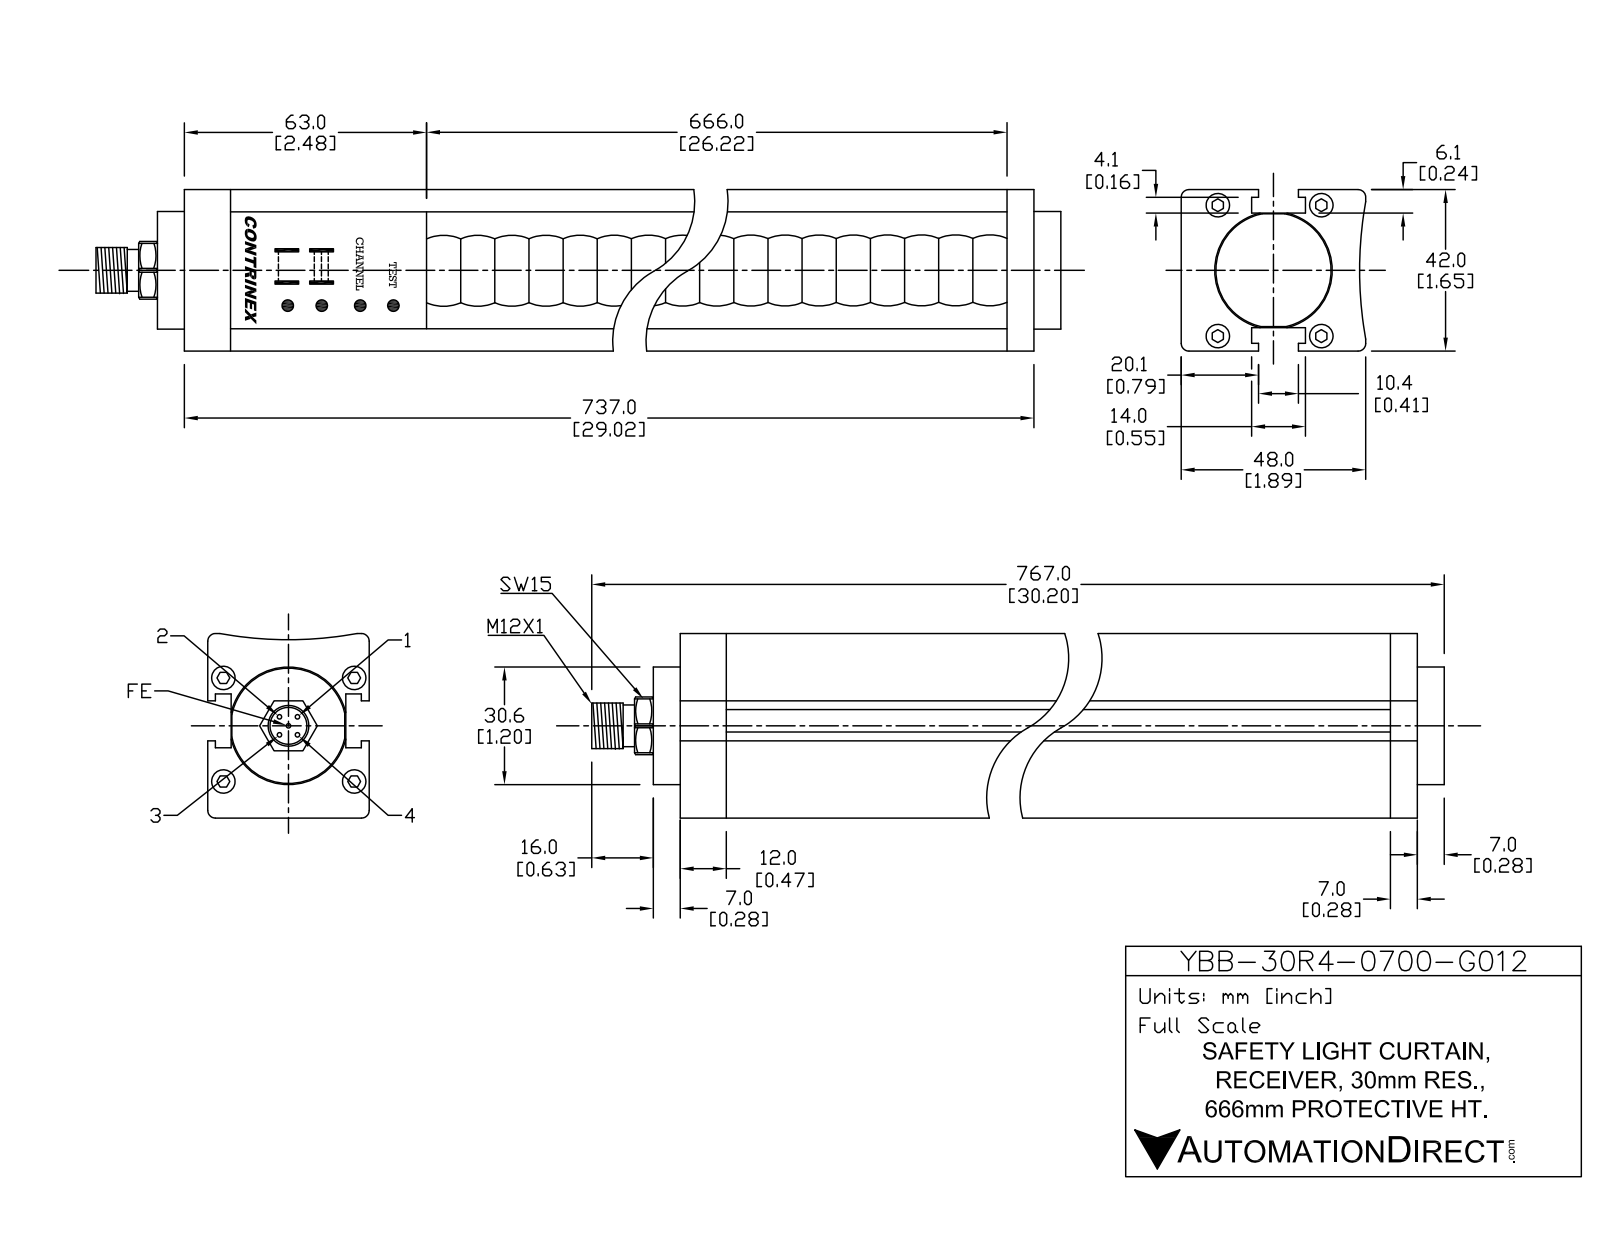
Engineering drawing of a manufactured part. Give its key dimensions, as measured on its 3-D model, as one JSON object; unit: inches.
{"part_name": "YBB-30R4-0700-G012", "step_written_by": "SolidWorks 2016 (AUTOMOTIVE_DESIGN)", "units": "inches", "bodies": {"solids": 19, "faces": 440, "planar": 208, "cylindrical": 168, "other": 64}, "overall_size": [30.197, 1.89, 1.654], "volume_in3": 81.16, "surface_area_in2": 271.1, "round_holes": [[0.236, 4], [0.335, 1], [1.26, 1]], "round_bosses_or_shafts": [[0.039, 5], [0.217, 4], [1.205, 1], [0.472, 1], [0.413, 1]], "partial_cylinders_radius": [[0.039, 48], [0.02, 4], [0.022, 2], [0.323, 1], [3.937, 1]], "face_to_face_distances": [0.248, 1.406, 1.654, 1.157, 0.551, 0.677, 1.228, 0.618, 1.169, 1.846], "hole_center_spacings": [0.828, 0.88, 1.059, 1.339, 1.707]}
